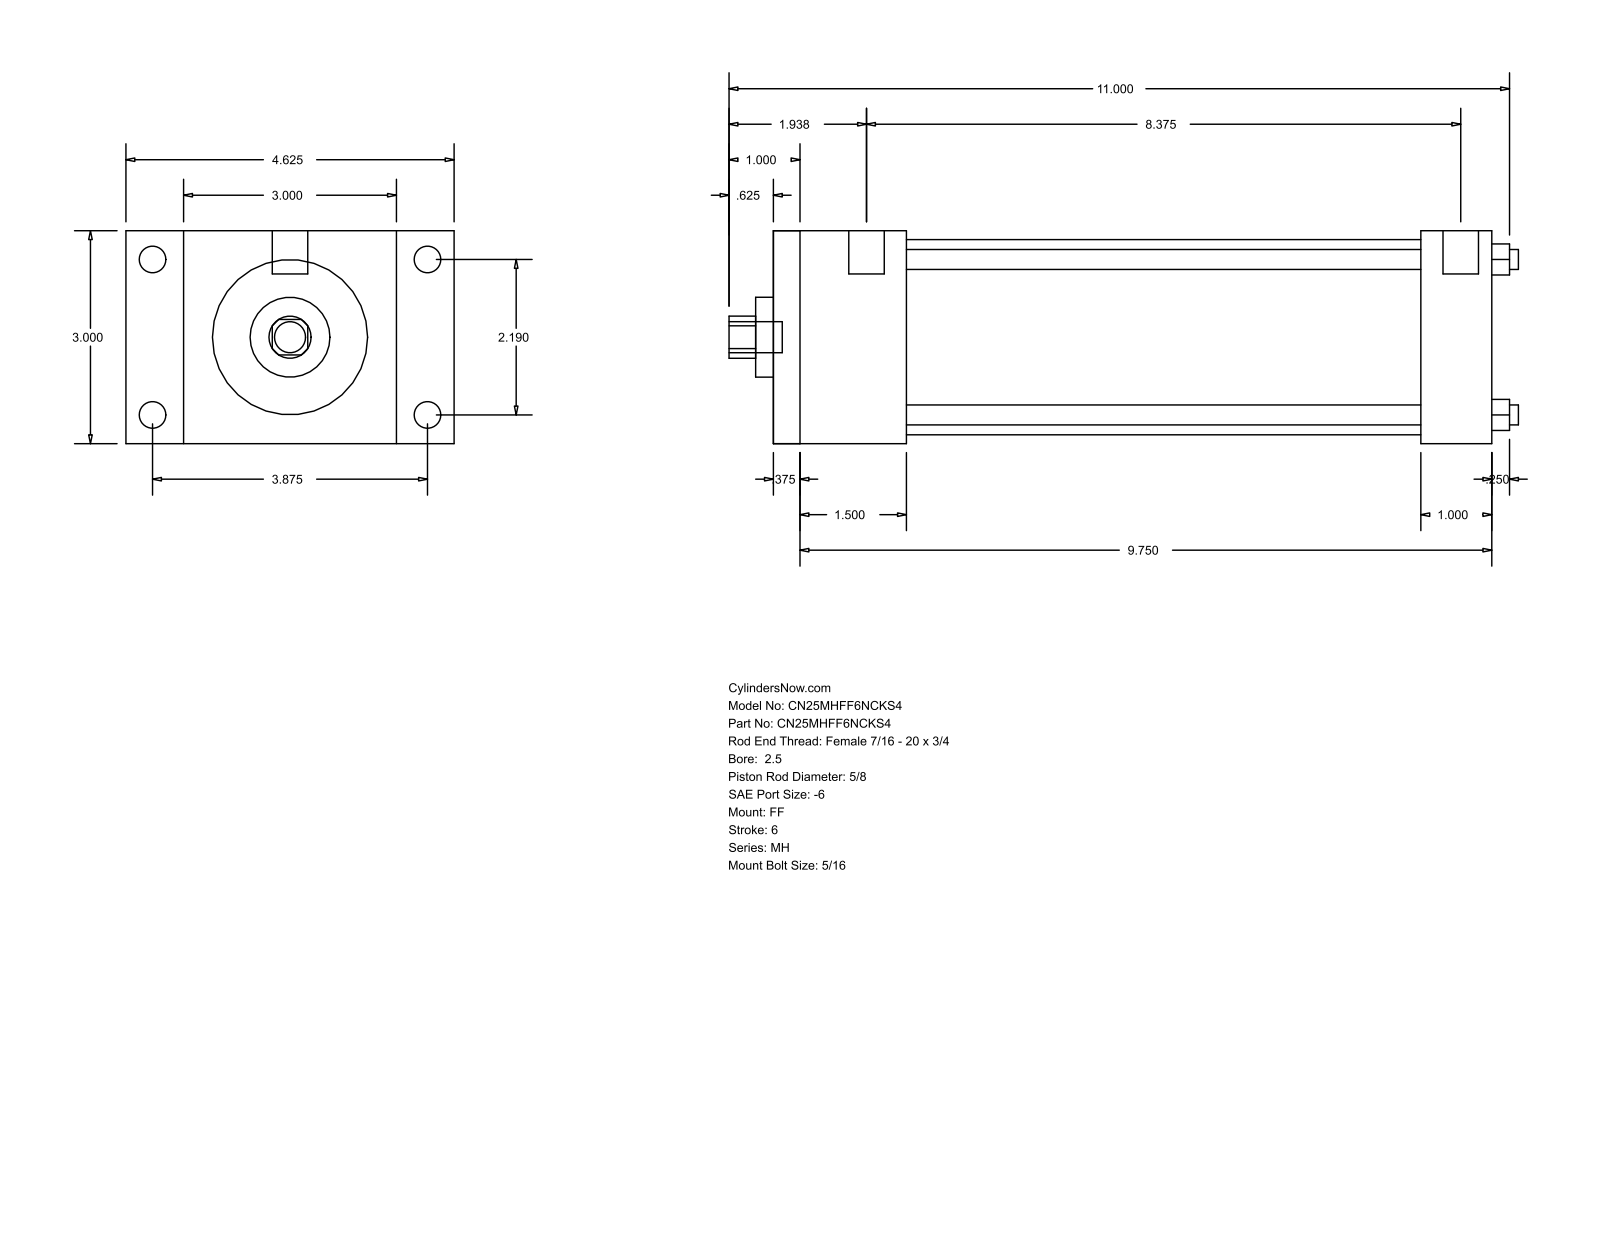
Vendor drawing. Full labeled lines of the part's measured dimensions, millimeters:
Part name (STEP PRODUCT): MH_FF__0250_0.625
STEP written by: GSSL Pune (CONFIG_CONTROL_DESIGN)
Units: millimetres
Bodies: 0 solids, 92 faces (64 planar, 28 cylindrical, 0 other)
Overall size (bounding box): 282.57 × 117.47 × 76.2
Round holes (diameter × count): ⌀7.14 ×4, ⌀15.88 ×1, ⌀28.57 ×1, ⌀69.85 ×1
Round bosses / shafts (diameter × count): ⌀9.53 ×4, ⌀5.56 ×4, ⌀12.7 ×2, ⌀11.11 ×1
Partial cylindrical surfaces — rounded edges, fillets, slot ends (radius × count): R7.54 ×1
Main face-to-face distances: 76.2, 257.17, 9.52, 247.65, 25.4, 47.62, 231.77, 38.1, 222.25, 184.15
Hole centre spacings: 39.33, 55.62, 78.66
